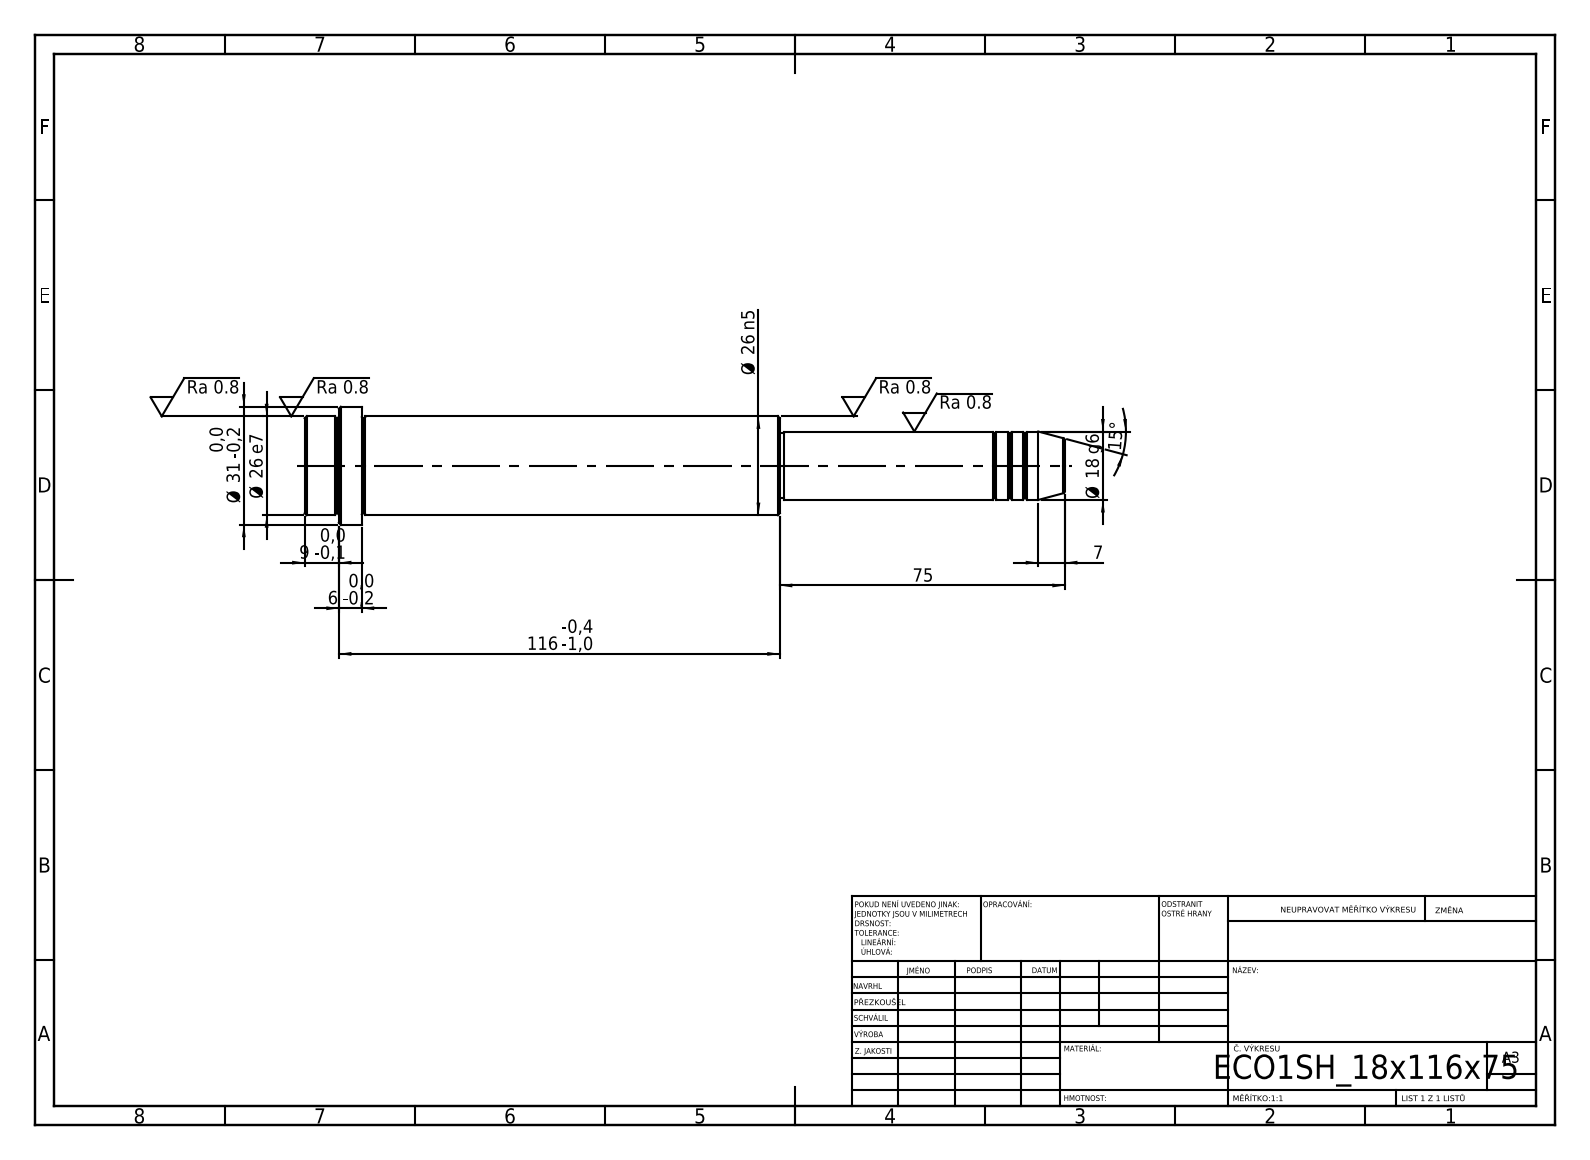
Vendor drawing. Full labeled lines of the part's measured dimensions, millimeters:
STEP written by: SolidWorks 2019 (CONFIG_CONTROL_DESIGN)
Units: millimetres
Bodies: 1 solid, 52 faces (6 planar, 16 cylindrical, 30 other)
Overall size (bounding box): 200 × 31 × 31
Volume: 86 260 mm³ · Surface area: 16 075 mm²
Round bosses / shafts (diameter × count): ⌀31 ×1, ⌀26 ×1, ⌀18 ×1, ⌀17 ×1
Main face-to-face distances: 125, 110, 15, 116, 6, 9, 75, 185, 191, 200
